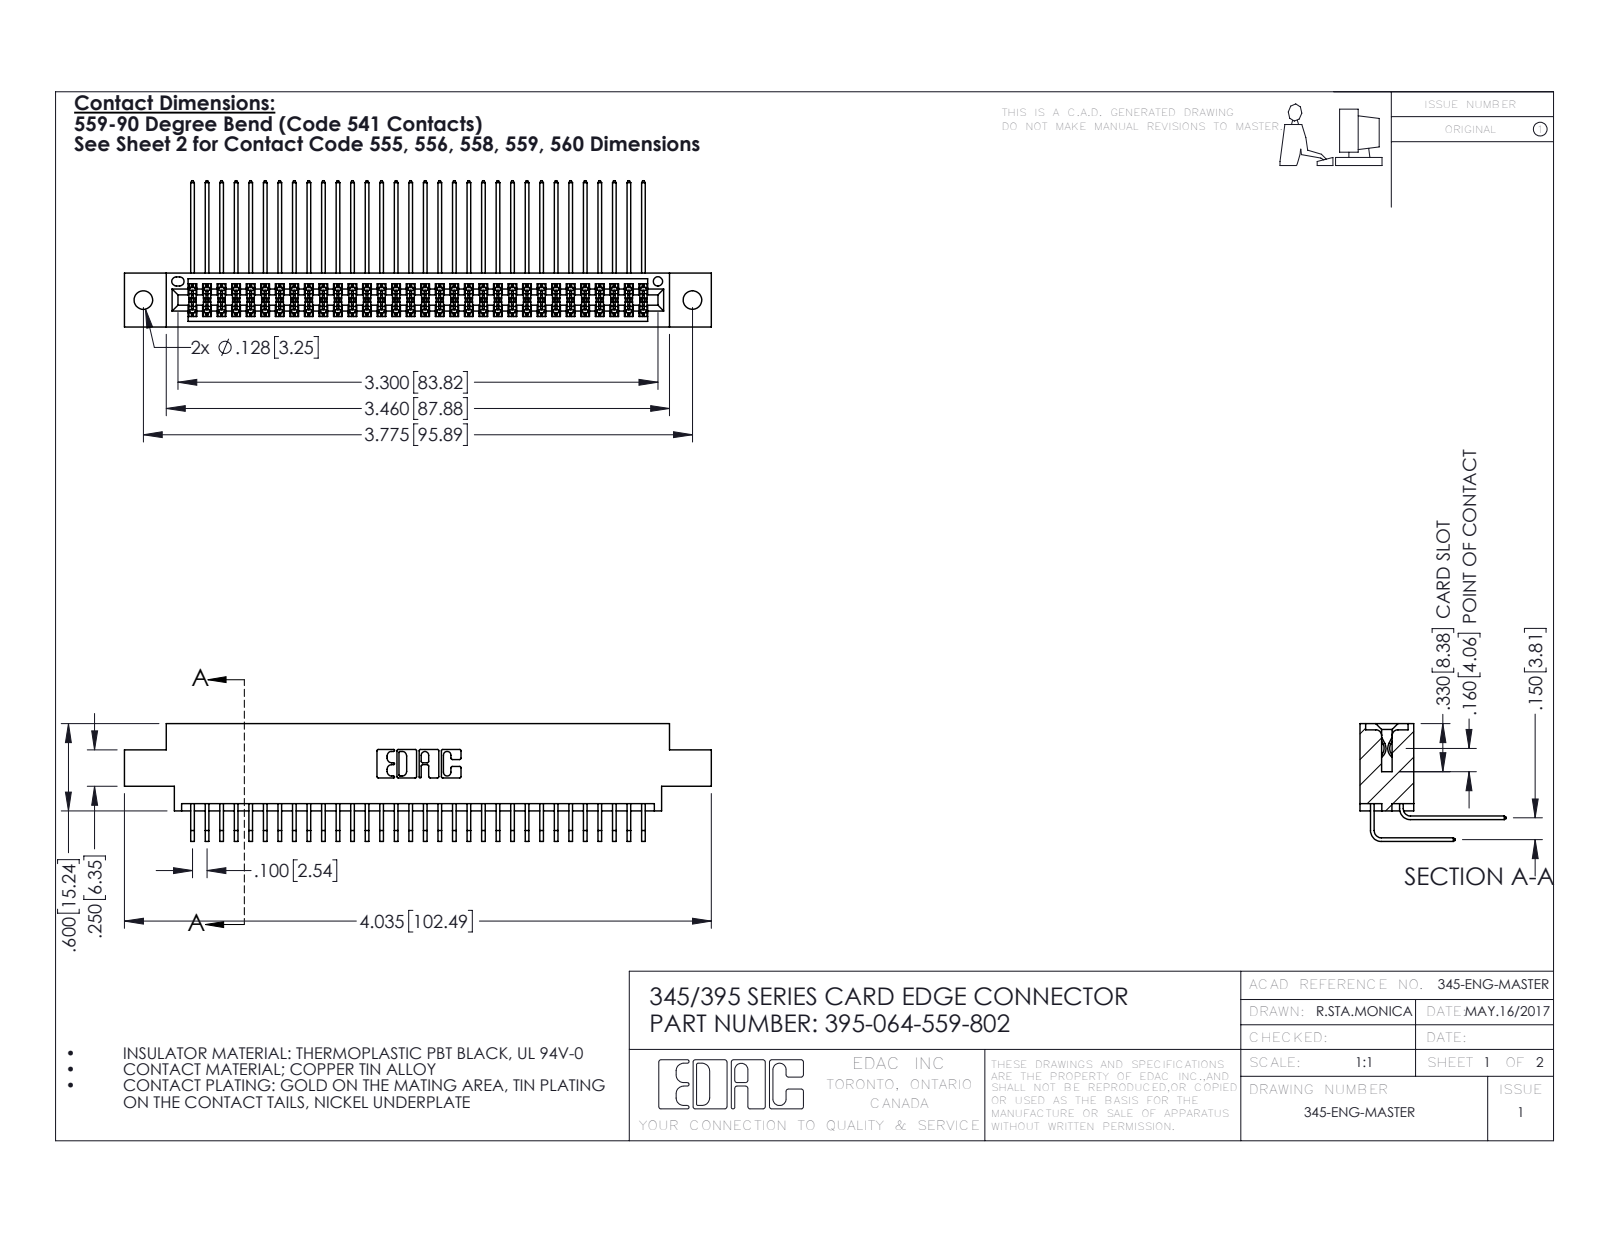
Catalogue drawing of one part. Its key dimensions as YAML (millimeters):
part_name: "395-064-559-802; 345-292-001_558 559 Tail - 1; 345-292-001_559 Tail - 2; 345 Part_0.170 Offset - 0.128 Dia"
step_written_by: "SolidWorks 2016 (CONFIG_CONTROL_DESIGN)"
units: millimeters
bodies: {solids: 65, faces: 3458, planar: 2324, cylindrical: 1134, other: 0}
overall_size: [102.5, 25.5, 20.5]
volume: 10100
surface_area: 16320
round_holes:
  - {diameter: 3.3, count: 2}
  - {diameter: 1.6, count: 1}
partial_cylinders:
  - {radius: 0.2, count: 96}
  - {radius: 0.3, count: 22}
  - {radius: 0.2, count: 6}
  - {radius: 0.8, count: 6}
  - {radius: 0.7, count: 3}
  - {radius: 0.4, count: 2}
  - {radius: 0.5, count: 2}
  - {radius: 0.6, count: 2}
face_to_face_distances: [1.8, 7.6, 9.4, 5.1, 2.5, 6.9, 0.6, 5.7, 4.4, 3.8]
hole_center_spacings: [6.9, 89.9, 95.9]
